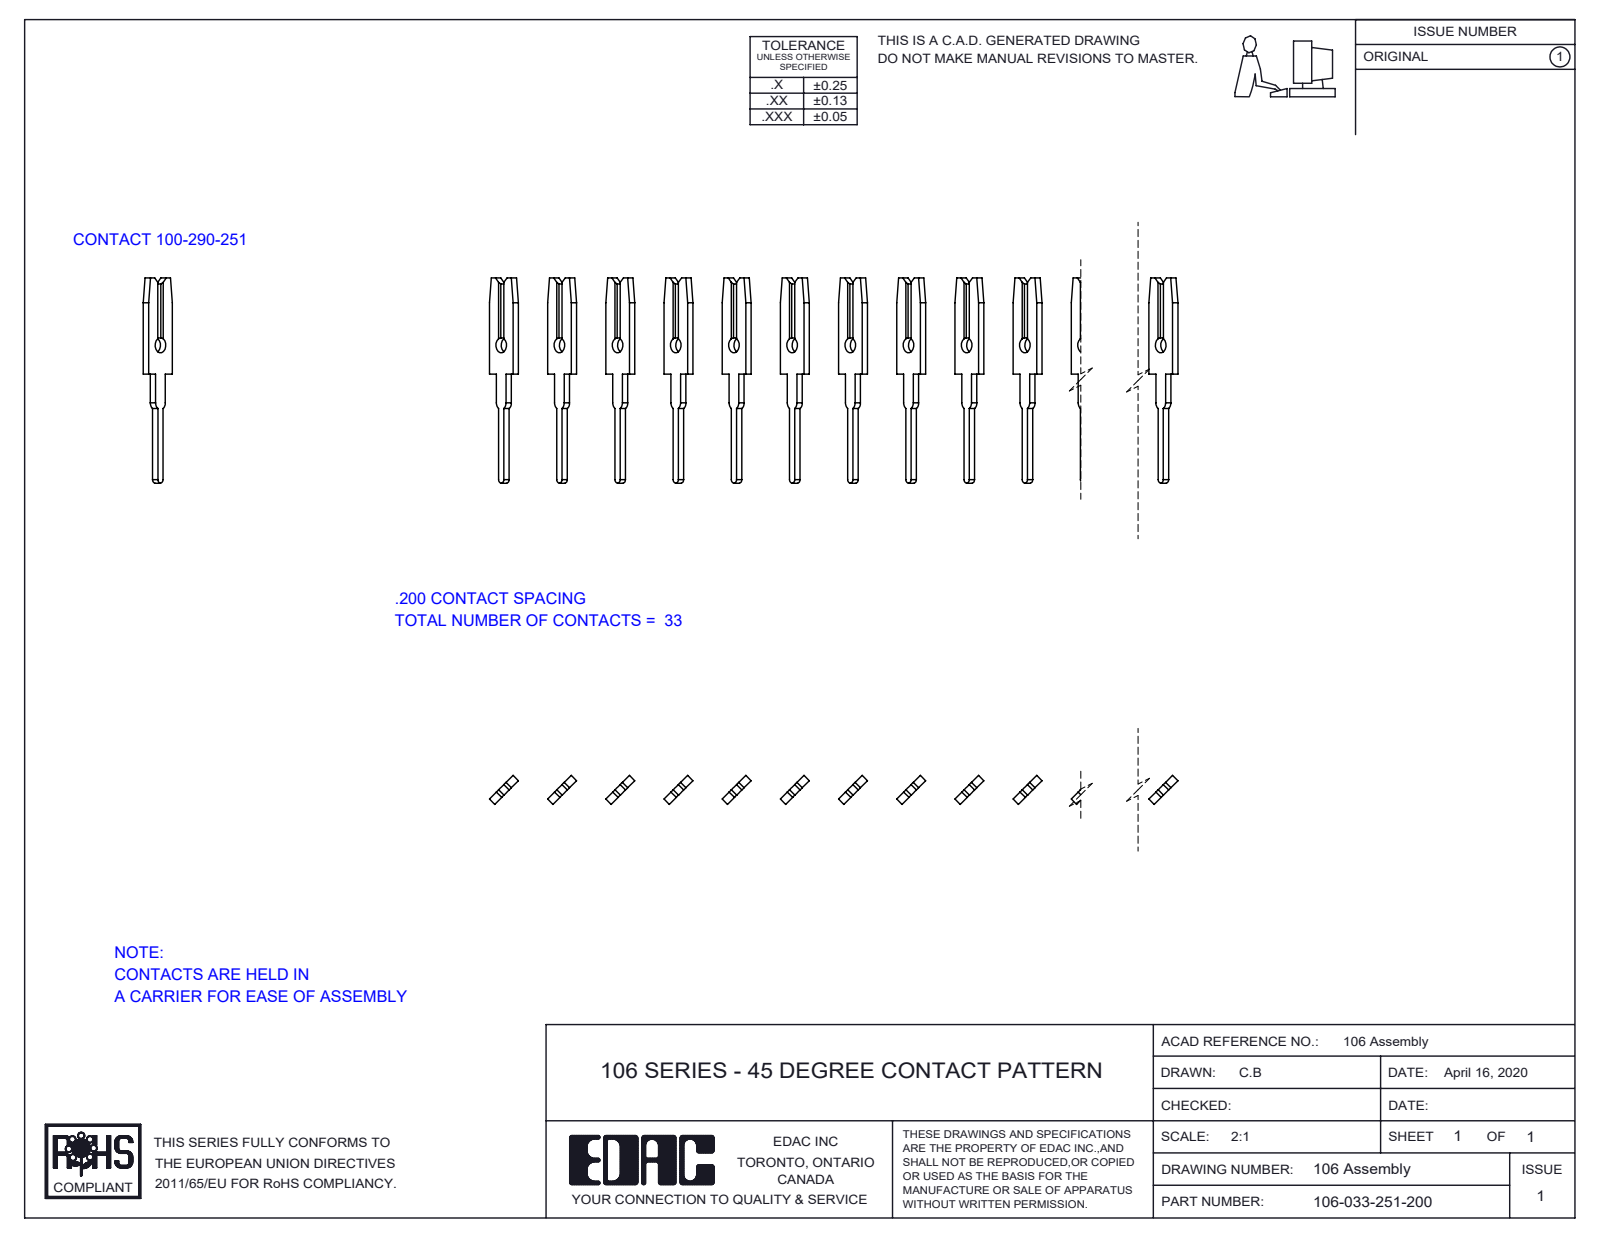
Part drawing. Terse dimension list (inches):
name: 100-290-001_100-290-251; 106-033-251-200
written by: SolidWorks 2016 (CONFIG_CONTROL_DESIGN)
unit: in
bodies: 33 solids, 924 faces (726 planar, 198 cylindrical, 0 other)
size: 6.5 × 0.705 × 0.1
volume: 0.037 in³; area: 4.597 in²
holes: 33× ⌀0.052
rounds: 33× R0.012, 33× R0.024
face distances: 0.141, 0.848, 0.707, 0.283, 0.99, 0.566, 0.424, 1.131, 0.424, 1.556
hole spacings: 0.141, 0.283, 0.424, 0.848, 1.839, 0.99, 1.556, 1.697
